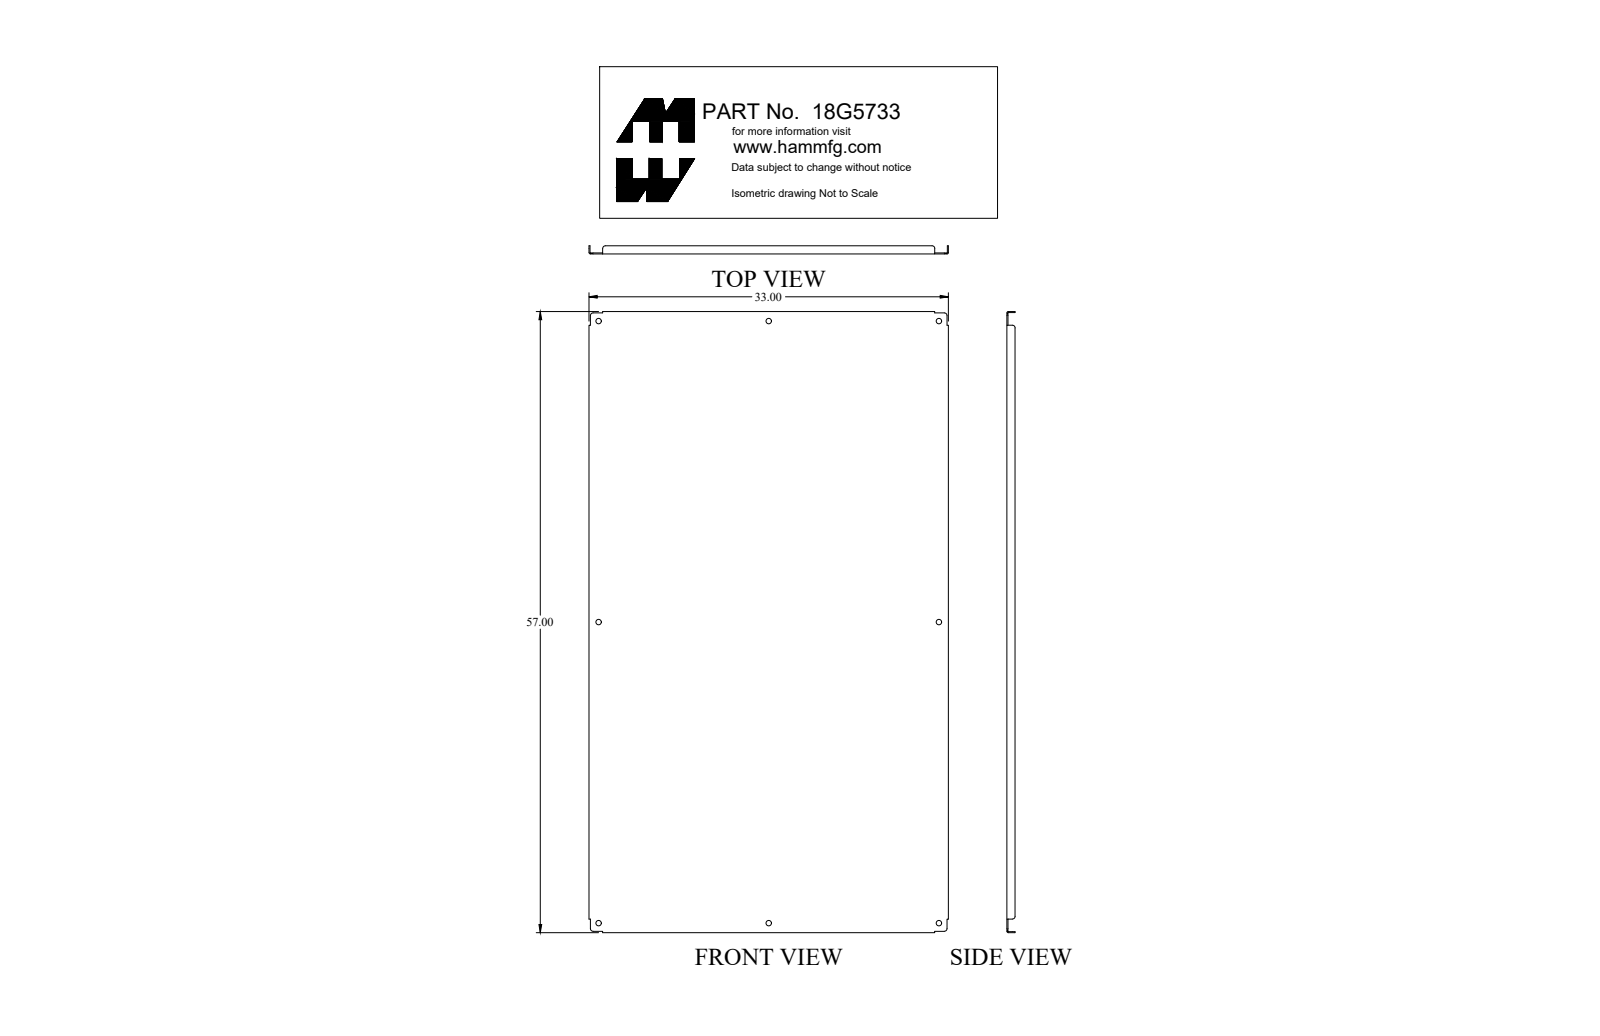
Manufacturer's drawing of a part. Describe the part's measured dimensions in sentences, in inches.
The part is named "18G5733_Default". Its 3-D file was written by "SolidWorks 2018 (CONFIG_CONTROL_DESIGN)". It is 1 solid with 66 faces: 30 planar, 36 cylindrical and 0 other. Overall it measures 57 by 33 by 0.75 inches. Its volume is 188.5 cubic inches and its surface area 3 986 square inches. Round holes: 8 of diameter 0.5. Partial cylindrical surfaces (rounded edges, fillets, slot ends): 8 of radius 0.25, 4 of radius 0.03, 4 of radius 0.125. The main face-to-face distances are 0.095, 32.905, 56.905, 32.81, 33, 57, 56.81, 0.75, 0.655, 0.125. The hole center spacings are 15.625, 27.625, 31.738, 41.71, 57.417, 31.25, 55.25, 63.475.
